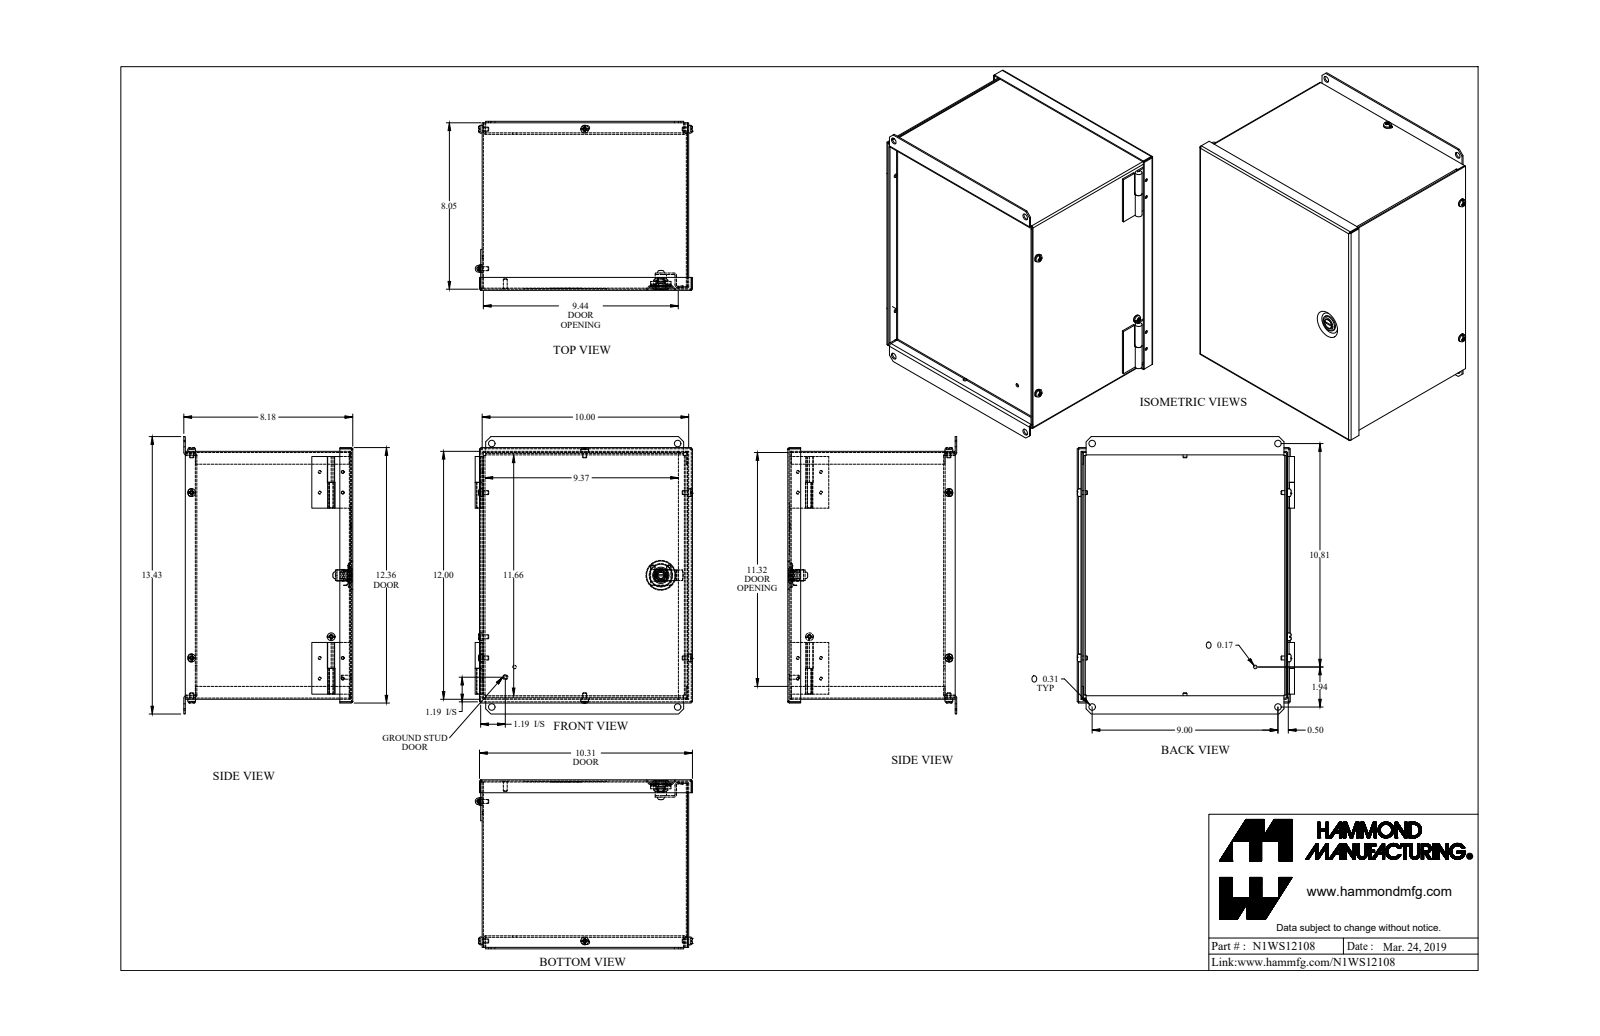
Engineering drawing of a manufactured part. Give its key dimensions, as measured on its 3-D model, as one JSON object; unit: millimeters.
{"part_name": "N1WS12108", "step_written_by": "SolidWorks 2018 (AUTOMOTIVE_DESIGN)", "units": "millimeters", "bodies": {"solids": 17, "faces": 607, "planar": 328, "cylindrical": 214, "other": 65}, "overall_size": [341, 267.2, 207.7], "volume_mm3": 682500, "surface_area_mm2": 892300, "round_holes": [[3.6, 8], [4.3, 5], [7.9, 4], [4.7, 1], [8.1, 1], [12.1, 1]], "round_bosses_or_shafts": [[3.3, 8], [9.5, 4], [4.8, 4], [20, 1], [13.9, 1], [12, 1], [11.9, 1], [9.3, 1]], "partial_cylinders_radius": [[0.7, 9], [2.2, 9], [0.9, 8], [2.7, 6], [2.8, 6], [0.3, 4], [2.5, 4], [2, 2]], "face_to_face_distances": [1.4, 252.6, 303.4, 1.8, 1.4, 192.1, 193.6, 190.3, 191.7, 254], "hole_center_spacings": [228.6, 25.4, 28.4, 38.1, 230.4, 203.2, 157.4, 159.4]}
